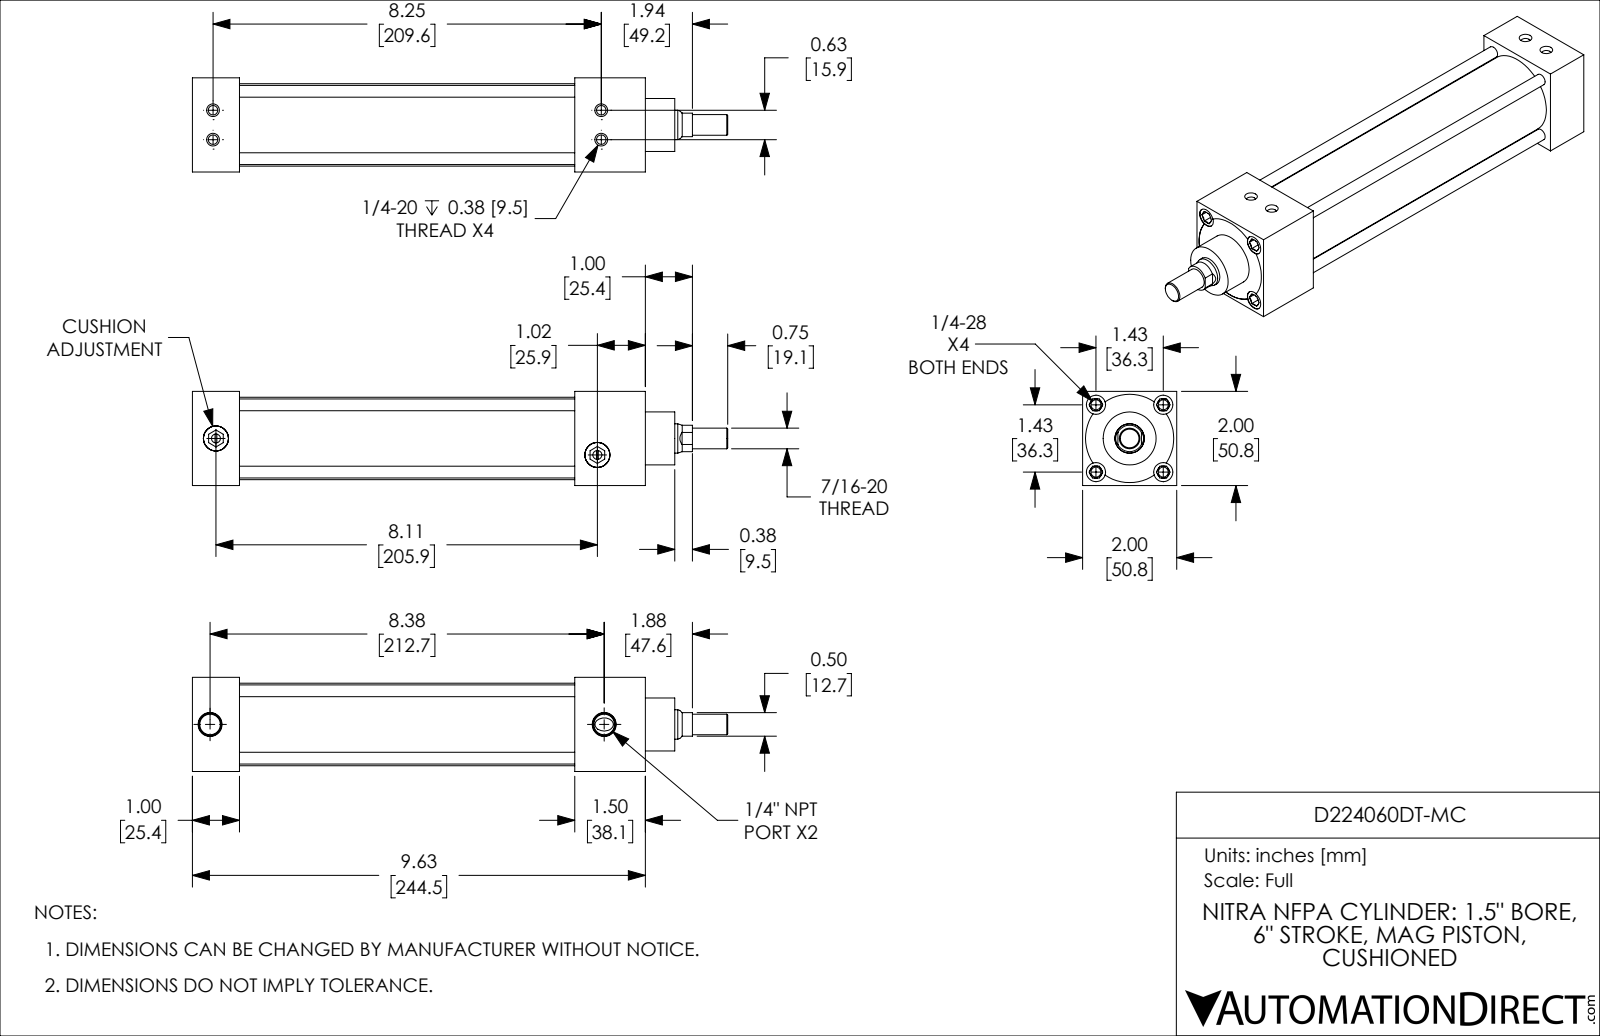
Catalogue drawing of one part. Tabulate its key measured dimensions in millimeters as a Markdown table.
| quantity | value |
| --- | --- |
| part name | D224060DT-MC; D224060DT-MC_PISTON_KK1; D224060DT-MC_CUSHION; D224060DT-MC_BODY |
| STEP written by | SolidWorks 2019 (CONFIG_CONTROL_DESIGN) |
| units | millimeters |
| bodies | 4 solids, 251 faces (90 planar, 81 cylindrical, 80 other) |
| overall size | 288.9 × 50.8 × 50.8 |
| volume | 328 100 mm³ |
| surface area | 110 200 mm² |
| round holes (diameter × count) | 5.1 × 4, 5.4 × 4, 10.3 × 4, 4.8 × 2, 11.1 × 2, 13.5 × 2, 15.9 × 1, 38.1 × 1 |
| round bosses / shafts (diameter × count) | 6.4 × 4, 13.5 × 2, 44.5 × 1, 38.1 × 1, 28.6 × 1, 15.8 × 1, 11.1 × 1 |
| partial cylindrical surfaces (radius × count) | 7.1 × 1, 23.8 × 1 |
| main face-to-face distances | 50.8, 25.4, 206.4, 181, 54, 244.3, 218.9, 38, 28.6, 152.4 |
| hole center spacings | 8.1, 25.7, 36.3, 15.9, 51.4, 209.6, 210.2, 211.3 |
